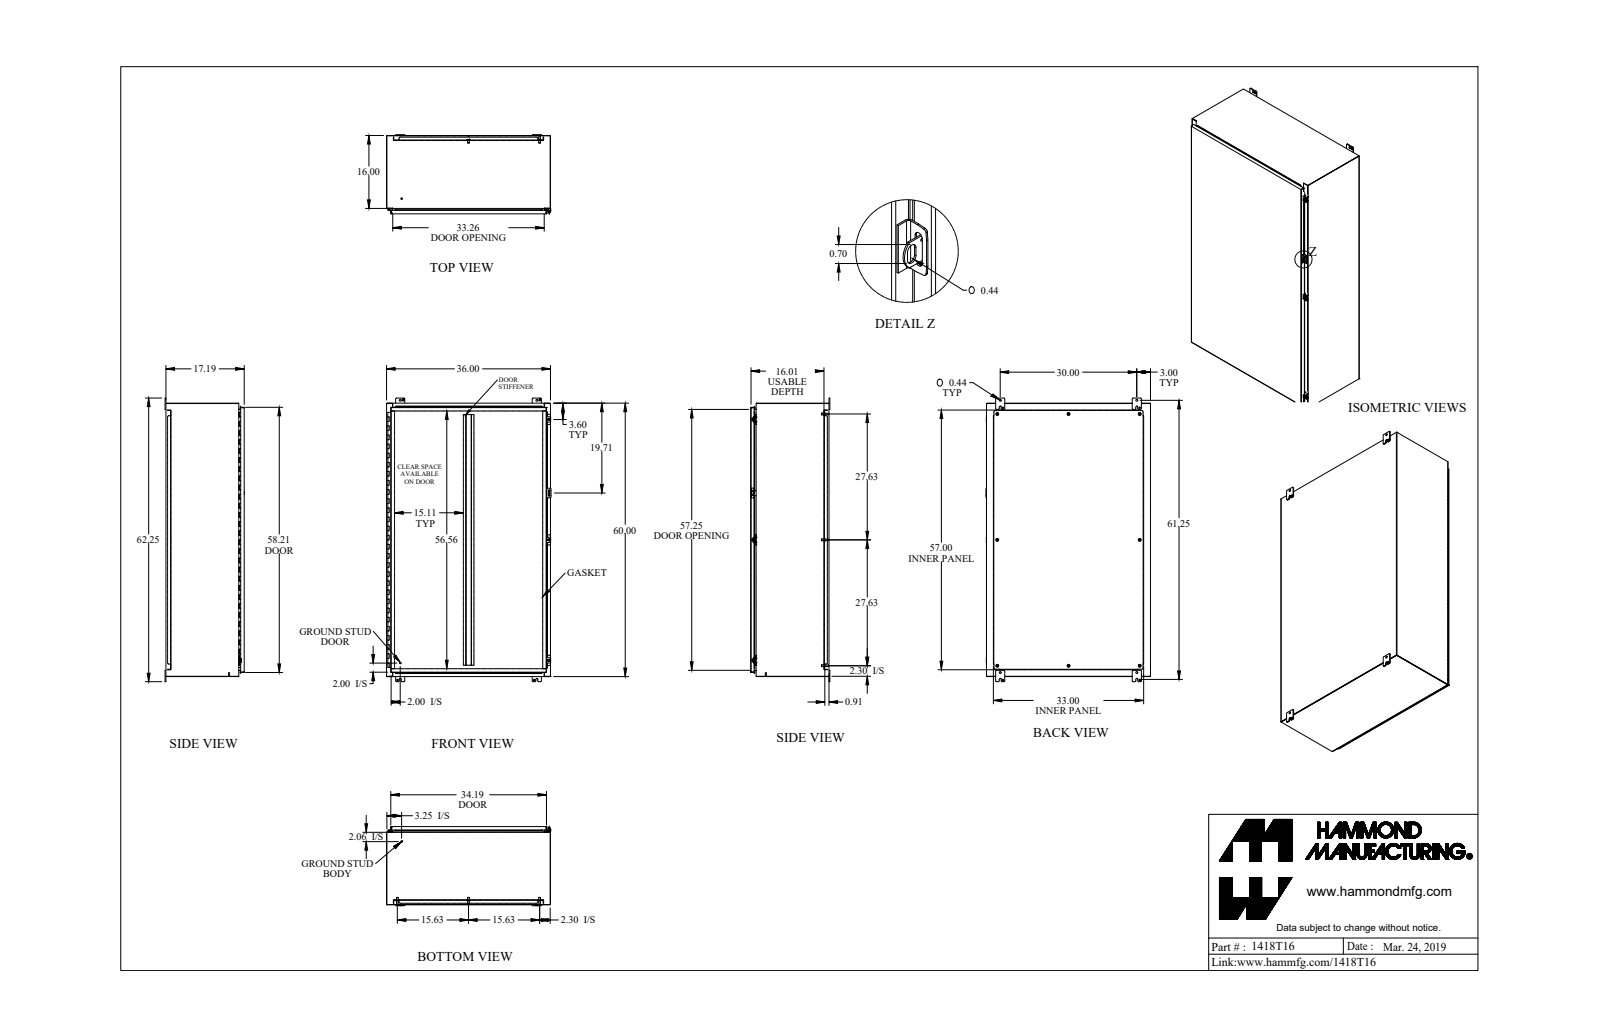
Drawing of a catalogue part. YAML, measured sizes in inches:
part_name: "1418T16_Default"
step_written_by: "SolidWorks 2019 (CONFIG_CONTROL_DESIGN)"
units: inches
bodies: {solids: 56, faces: 1796, planar: 1043, cylindrical: 675, other: 78}
overall_size: [62.25, 36.125, 17.437]
volume: 827.8
surface_area: 21589
round_holes:
  - {diameter: 0.5, count: 8}
  - {diameter: 0.307, count: 4}
  - {diameter: 0.313, count: 4}
  - {diameter: 0.437, count: 4}
  - {diameter: 0.445, count: 4}
  - {diameter: 0.213, count: 3}
  - {diameter: 0.265, count: 3}
  - {diameter: 0.375, count: 3}
  - {diameter: 0.125, count: 1}
  - {diameter: 0.187, count: 1}
round_bosses_or_shafts:
  - {diameter: 0.65, count: 8}
  - {diameter: 0.375, count: 8}
  - {diameter: 0.33, count: 8}
  - {diameter: 1, count: 4}
  - {diameter: 0.5, count: 3}
  - {diameter: 0.39, count: 3}
  - {diameter: 0.244, count: 3}
  - {diameter: 0.281, count: 2}
partial_cylinders:
  - {radius: 0.188, count: 34}
  - {radius: 0.036, count: 22}
  - {radius: 0.108, count: 22}
  - {radius: 0.25, count: 20}
  - {radius: 0.048, count: 19}
  - {radius: 0.143, count: 19}
  - {radius: 0.116, count: 16}
  - {radius: 0.125, count: 8}
face_to_face_distances: [0.072, 17.113, 17.041, 0.937, 17.185, 0.095, 1.009, 35.928, 16.081, 16.009]
hole_center_spacings: [15.625, 27.625, 57.417, 63.475, 30, 31.25, 41.71, 55.25]
